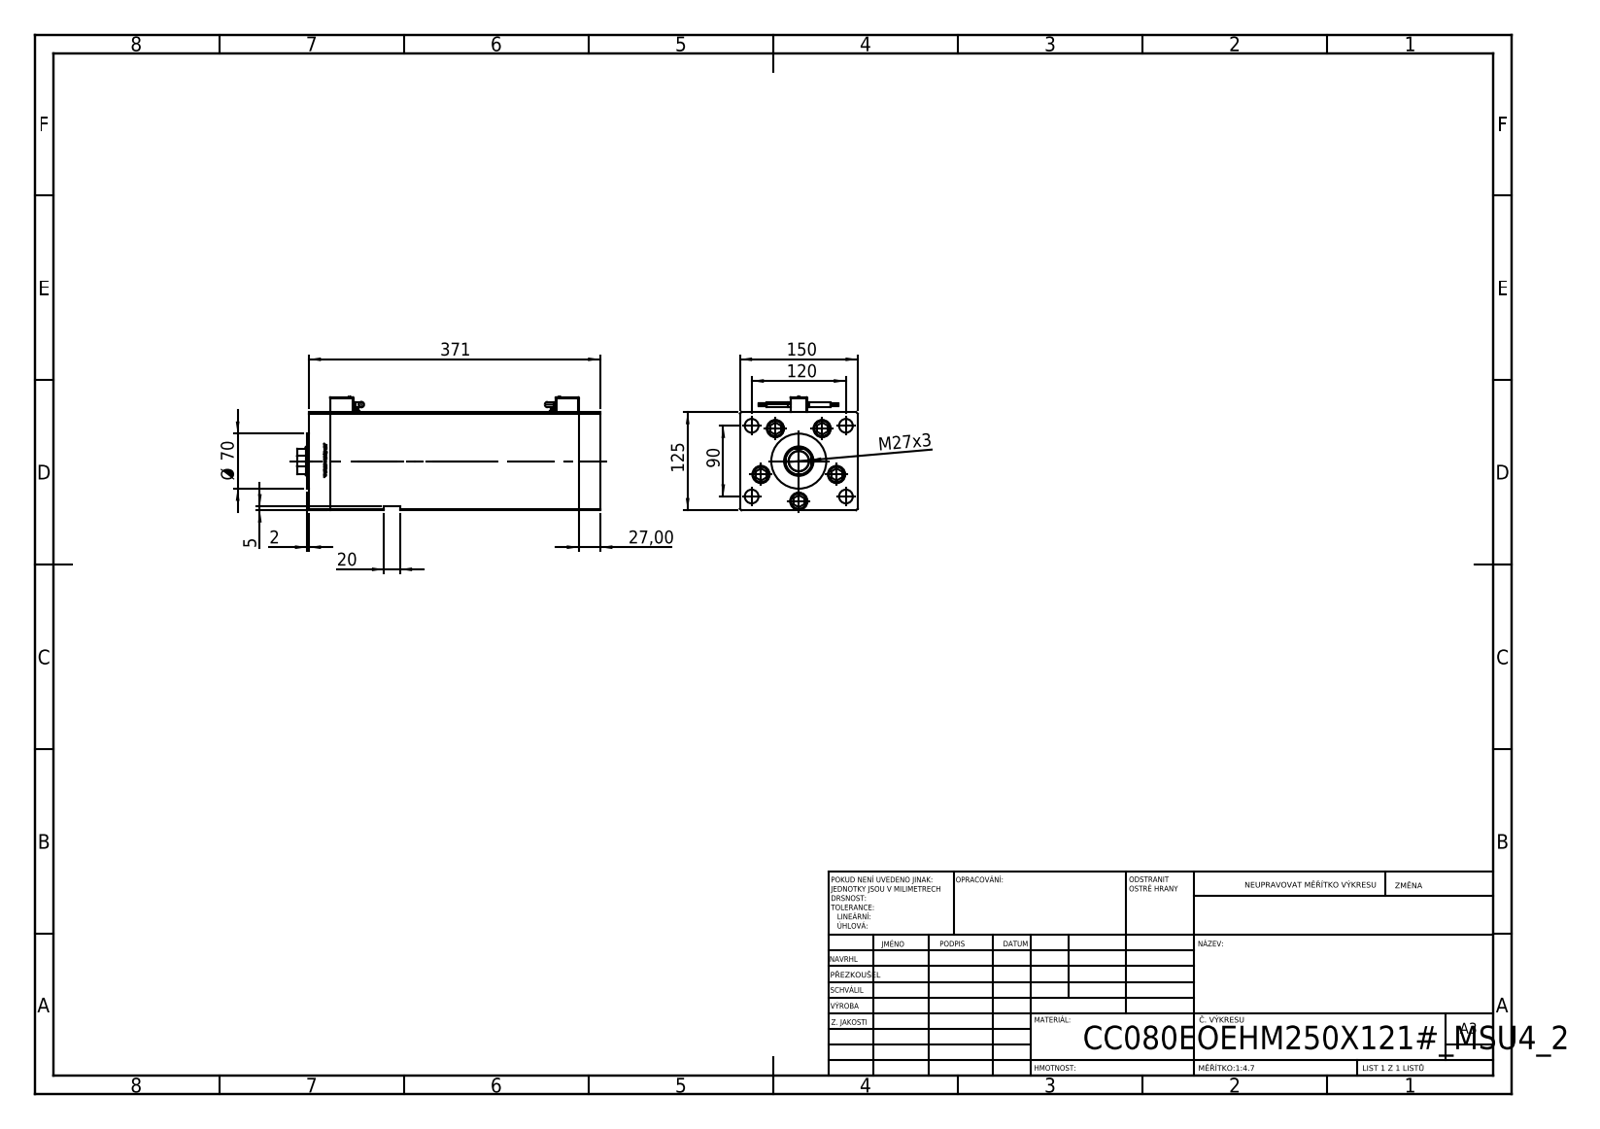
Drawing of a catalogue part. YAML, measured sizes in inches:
part_name: "V220C BACK_E; V220C_FRONT_E; Magnetic_Switch_MSU4; ALLEN BOLT (+2 more)"
step_written_by: "SolidWorks 2019 (CONFIG_CONTROL_DESIGN)"
units: inches
bodies: {solids: 16, faces: 1418, planar: 553, cylindrical: 255, other: 610}
overall_size: [15.197, 5.906, 5.713]
volume: 344.2
surface_area: 850
round_holes:
  - {diameter: 0.689, count: 9}
  - {diameter: 0.866, count: 5}
  - {diameter: 0.669, count: 4}
  - {diameter: 0.906, count: 4}
  - {diameter: 0.079, count: 2}
  - {diameter: 0.142, count: 2}
  - {diameter: 0.197, count: 2}
  - {diameter: 0.276, count: 2}
  - {diameter: 0.518, count: 2}
  - {diameter: 1.004, count: 1}
  - {diameter: 1.417, count: 1}
  - {diameter: 1.476, count: 1}
round_bosses_or_shafts:
  - {diameter: 0.033, count: 8}
  - {diameter: 0.827, count: 5}
  - {diameter: 0.315, count: 5}
  - {diameter: 0.276, count: 4}
  - {diameter: 0.236, count: 2}
  - {diameter: 0.138, count: 2}
  - {diameter: 0.098, count: 2}
  - {diameter: 3.15, count: 1}
partial_cylinders:
  - {radius: 0.039, count: 24}
  - {radius: 0.157, count: 4}
  - {radius: 0.037, count: 2}
  - {radius: 0.689, count: 1}
face_to_face_distances: [4.921, 5.906, 1.063, 12.48, 13.543, 0.256, 1.319, 14.606, 12.224, 13.287]
hole_center_spacings: [2.008, 2.953, 0.325, 1.198, 1.2, 2.177, 2.234, 2.319]
